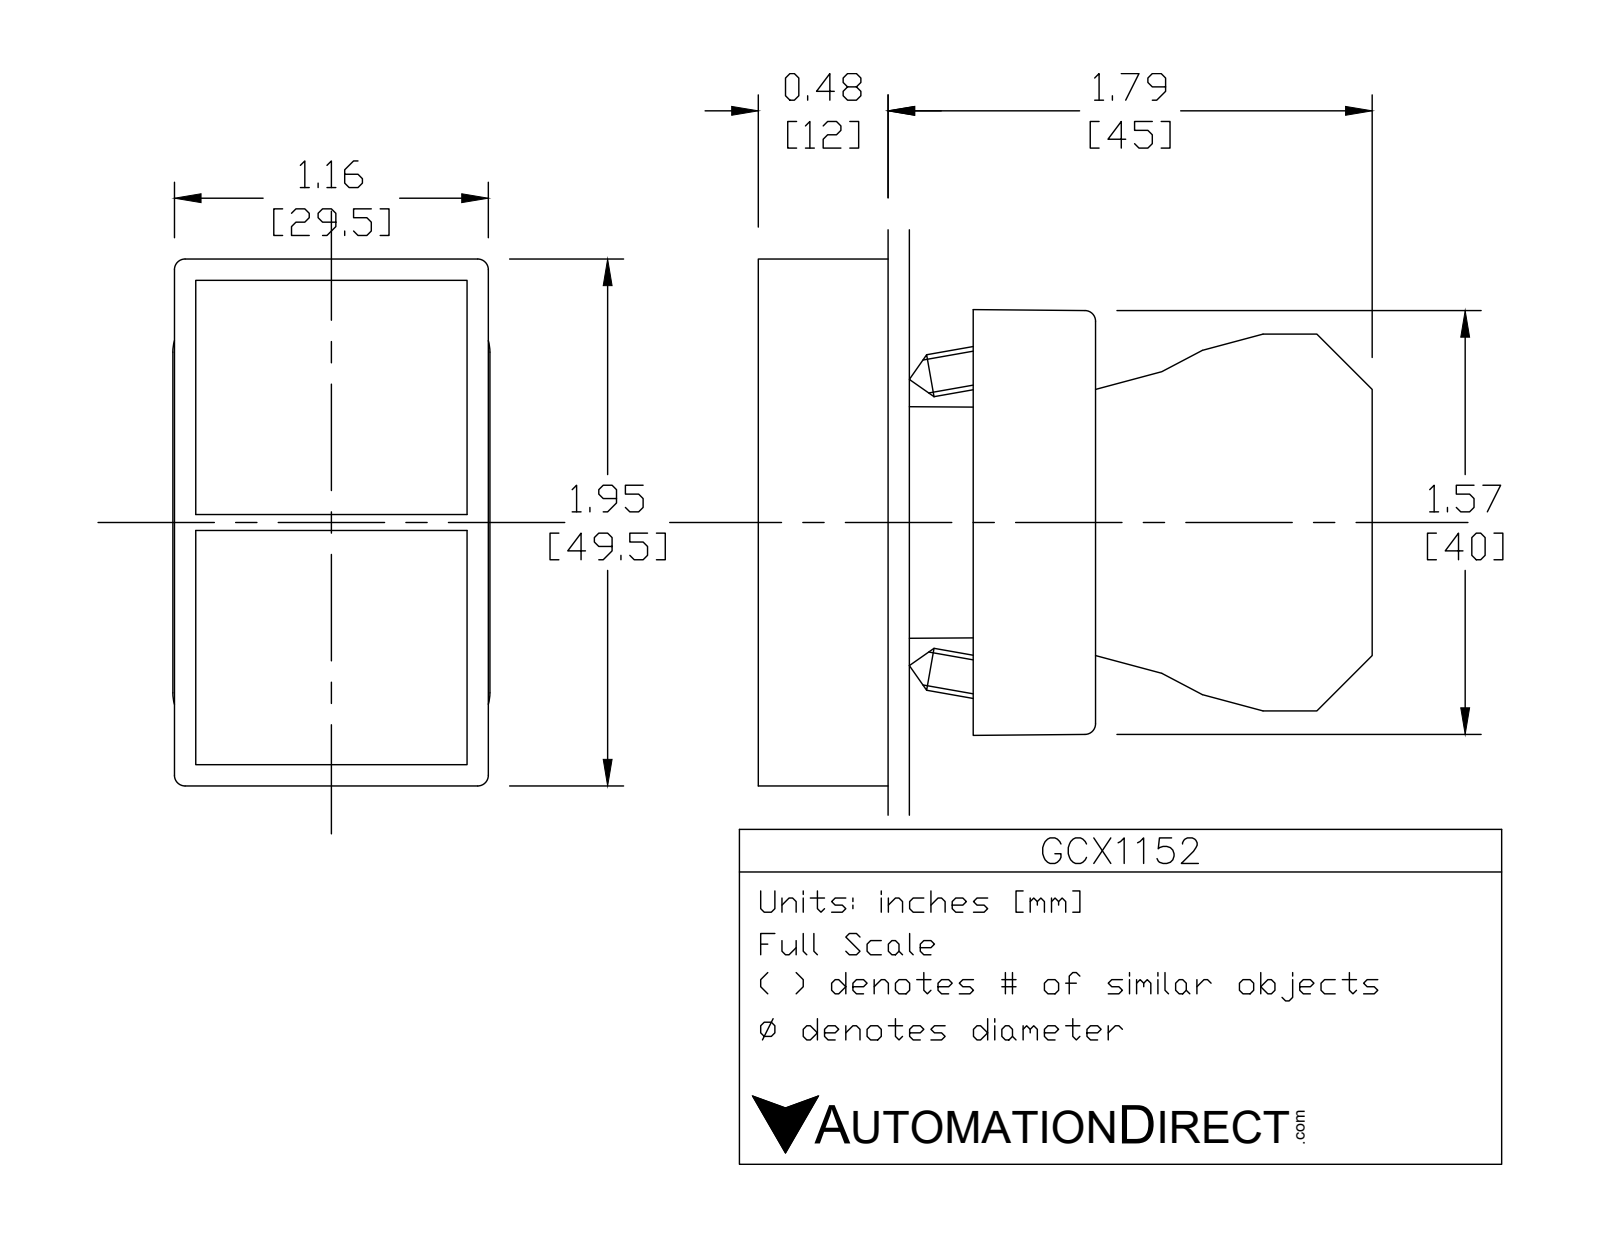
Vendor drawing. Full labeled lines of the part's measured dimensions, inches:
Part name (STEP PRODUCT): GCX1152; ecx1030; ecx1040; GCX1152 OPERATOR (+1 more)
STEP written by: SolidWorks 2016 (AUTOMOTIVE_DESIGN)
Units: inches
Bodies: 8 solids, 495 faces (322 planar, 144 cylindrical, 29 other)
Overall size (bounding box): 2.217 × 1.949 × 1.177
Volume: 2.922 in³ · Surface area: 43.02 in²
Round holes (diameter × count): ⌀0.079 ×4, ⌀0.087 ×2, ⌀0.124 ×2, ⌀0.13 ×2, ⌀0.197 ×1, ⌀0.709 ×1, ⌀0.878 ×1, ⌀0.888 ×1
Round bosses / shafts (diameter × count): ⌀0.157 ×2, ⌀0.945 ×1, ⌀0.856 ×1, ⌀0.78 ×1, ⌀0.591 ×1
Partial cylindrical surfaces — rounded edges, fillets, slot ends (radius × count): R0.059 ×24, R0.041 ×12, R0.124 ×12, R0.157 ×12, R0.039 ×4, R0.063 ×2, R0.079 ×2, R0.128 ×2
Main face-to-face distances: 0.02, 0.039, 0.531, 0.059, 0.579, 0.598, 0.591, 0.74, 1.193, 0.453
Hole centre spacings: 0.236, 0.544, 1.008, 0.98, 0.472, 0.49, 0.54, 0.674
